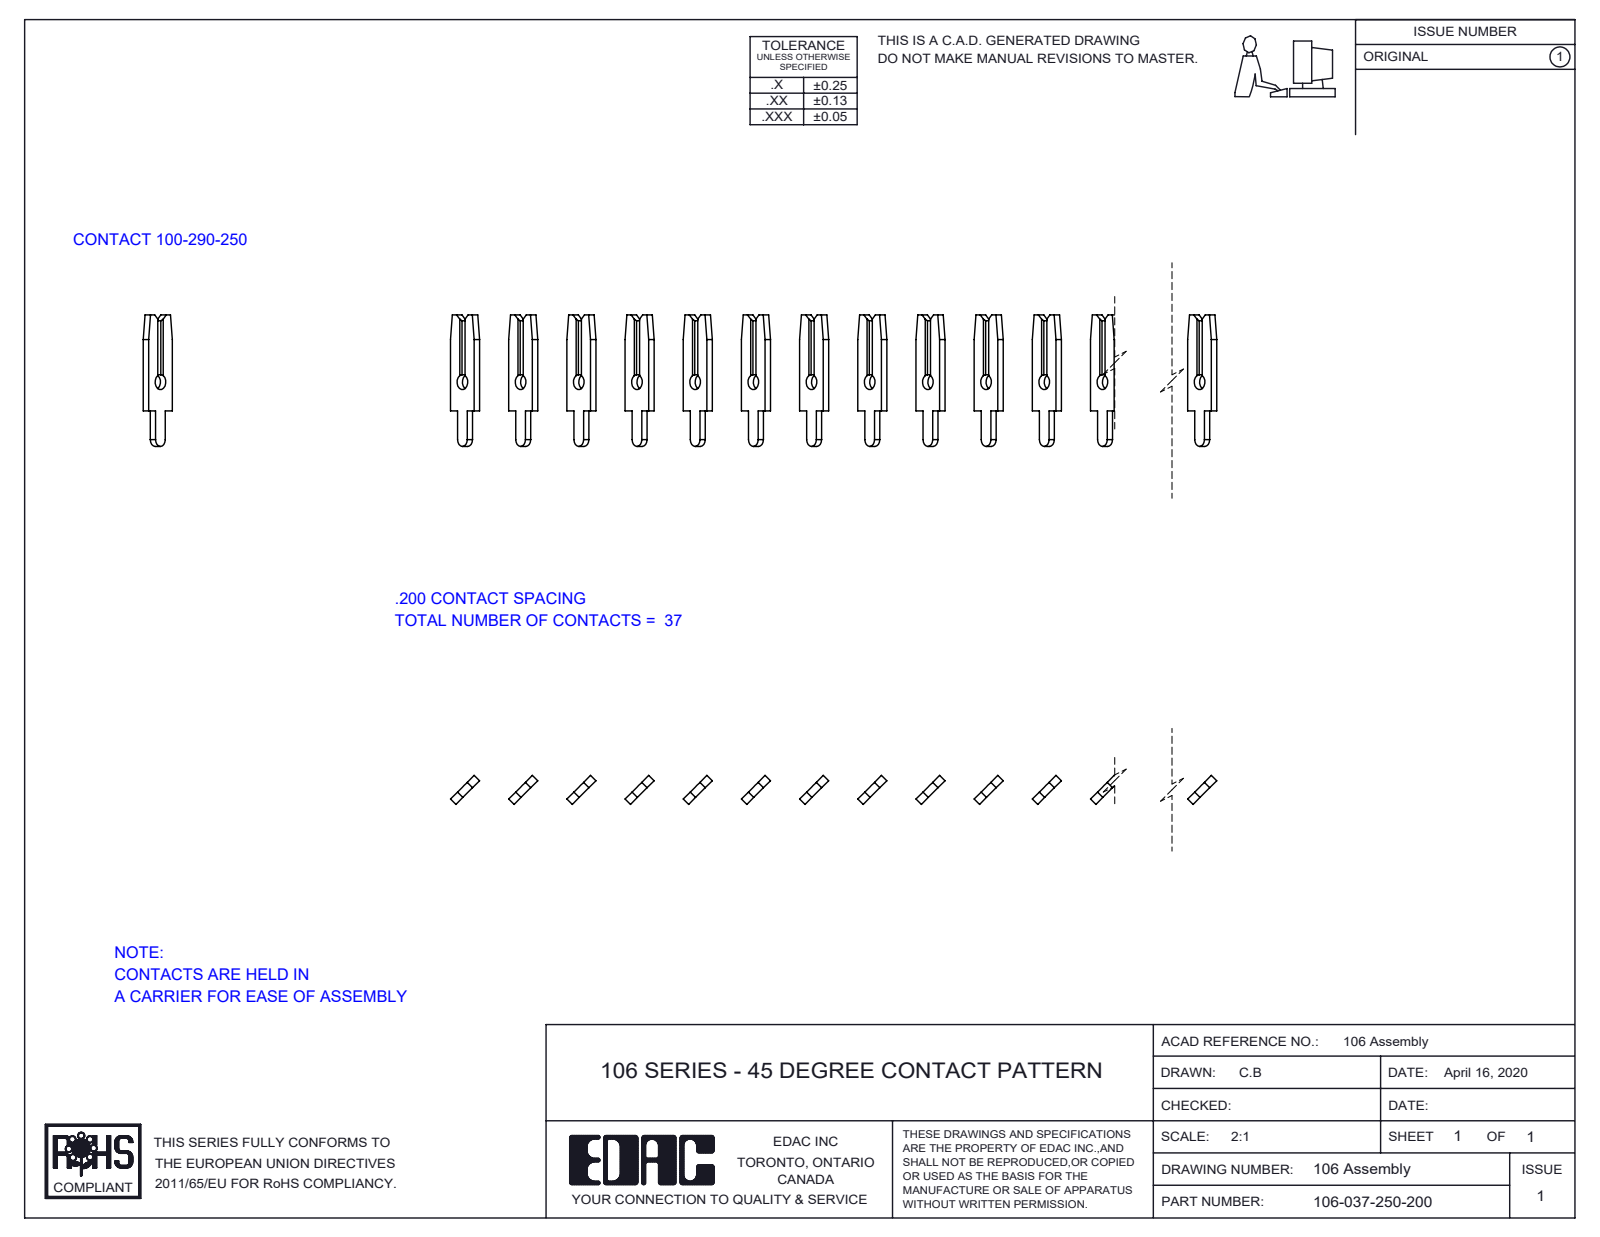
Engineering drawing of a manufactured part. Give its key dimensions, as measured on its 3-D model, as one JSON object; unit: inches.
{"part_name": "100-290-001_100-290-250; 106-037-250-200", "step_written_by": "SolidWorks 2016 (CONFIG_CONTROL_DESIGN)", "units": "inches", "bodies": {"solids": 37, "faces": 888, "planar": 740, "cylindrical": 148, "other": 0}, "overall_size": [7.3, 0.452, 0.1], "volume_in3": 0.035, "surface_area_in2": 4.207, "round_holes": [[0.052, 37]], "partial_cylinders_radius": [[0.024, 37]], "face_to_face_distances": [0.141, 0.848, 0.707, 0.283, 0.99, 0.566, 0.424, 1.131, 0.424, 1.556], "hole_center_spacings": [0.141, 0.283, 0.424, 0.848, 1.839, 0.99, 1.556, 1.697]}
